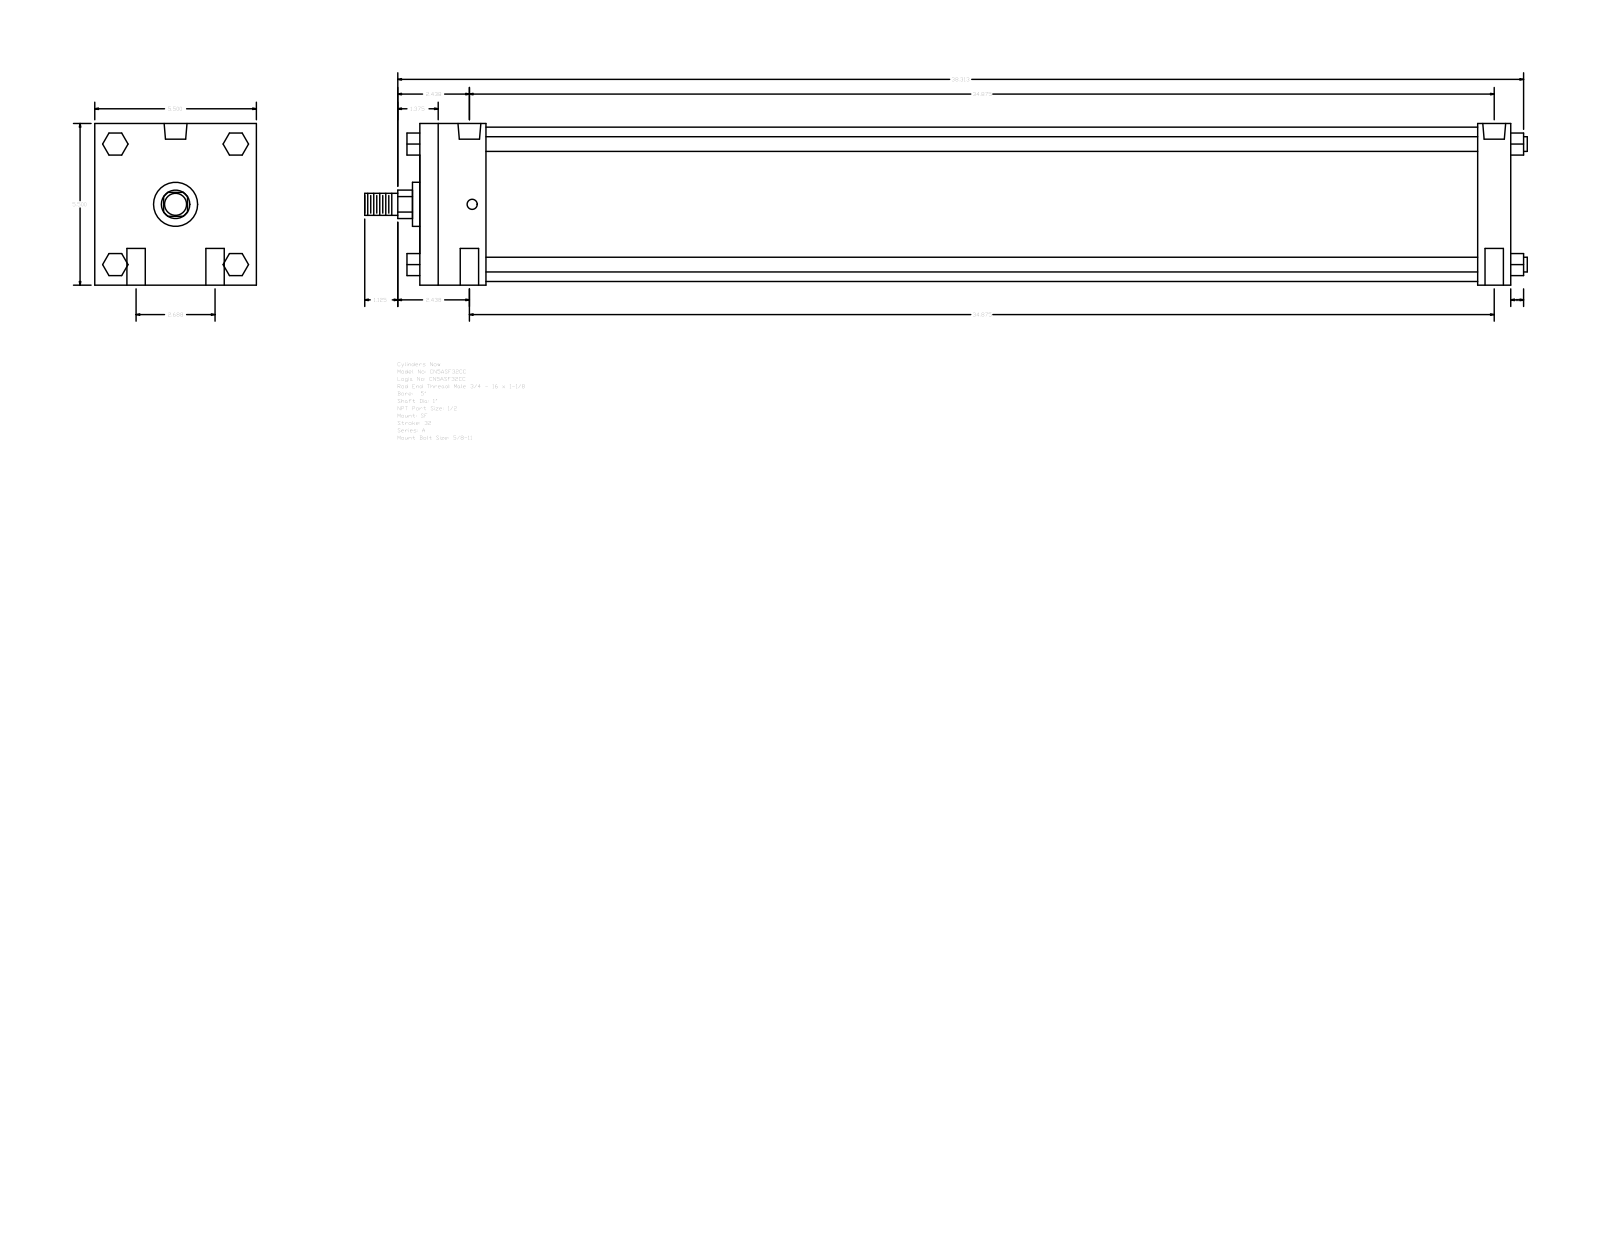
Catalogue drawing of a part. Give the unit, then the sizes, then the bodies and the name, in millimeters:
Units: millimetres
Overall size (bounding box): 1004.89 × 139.7 × 139.7
Round holes (diameter × count): ⌀15.88 ×4, ⌀8.73 ×2, ⌀19.77 ×2
Round bosses / shafts (diameter × count): ⌀12.7 ×4, ⌀133.35 ×1, ⌀38.1 ×1, ⌀25.4 ×1, ⌀19.05 ×1
Partial cylindrical surfaces — rounded edges, fillets, slot ends (radius × count): R12.29 ×1
Main face-to-face distances: 139.7, 942.97, 28.57, 57.15, 914.4, 857.25, 885.82, 19.05, 52.07, 90.18
Hole centre spacings: 34.13, 886.49, 885.83, 68.26, 888.46, 881.05
Bodies: 0 solids, 124 faces (94 planar, 30 cylindrical, 0 other)
Part name (STEP PRODUCT): A_SF__0500_1
STEP written by: GSSL Pune (CONFIG_CONTROL_DESIGN)
